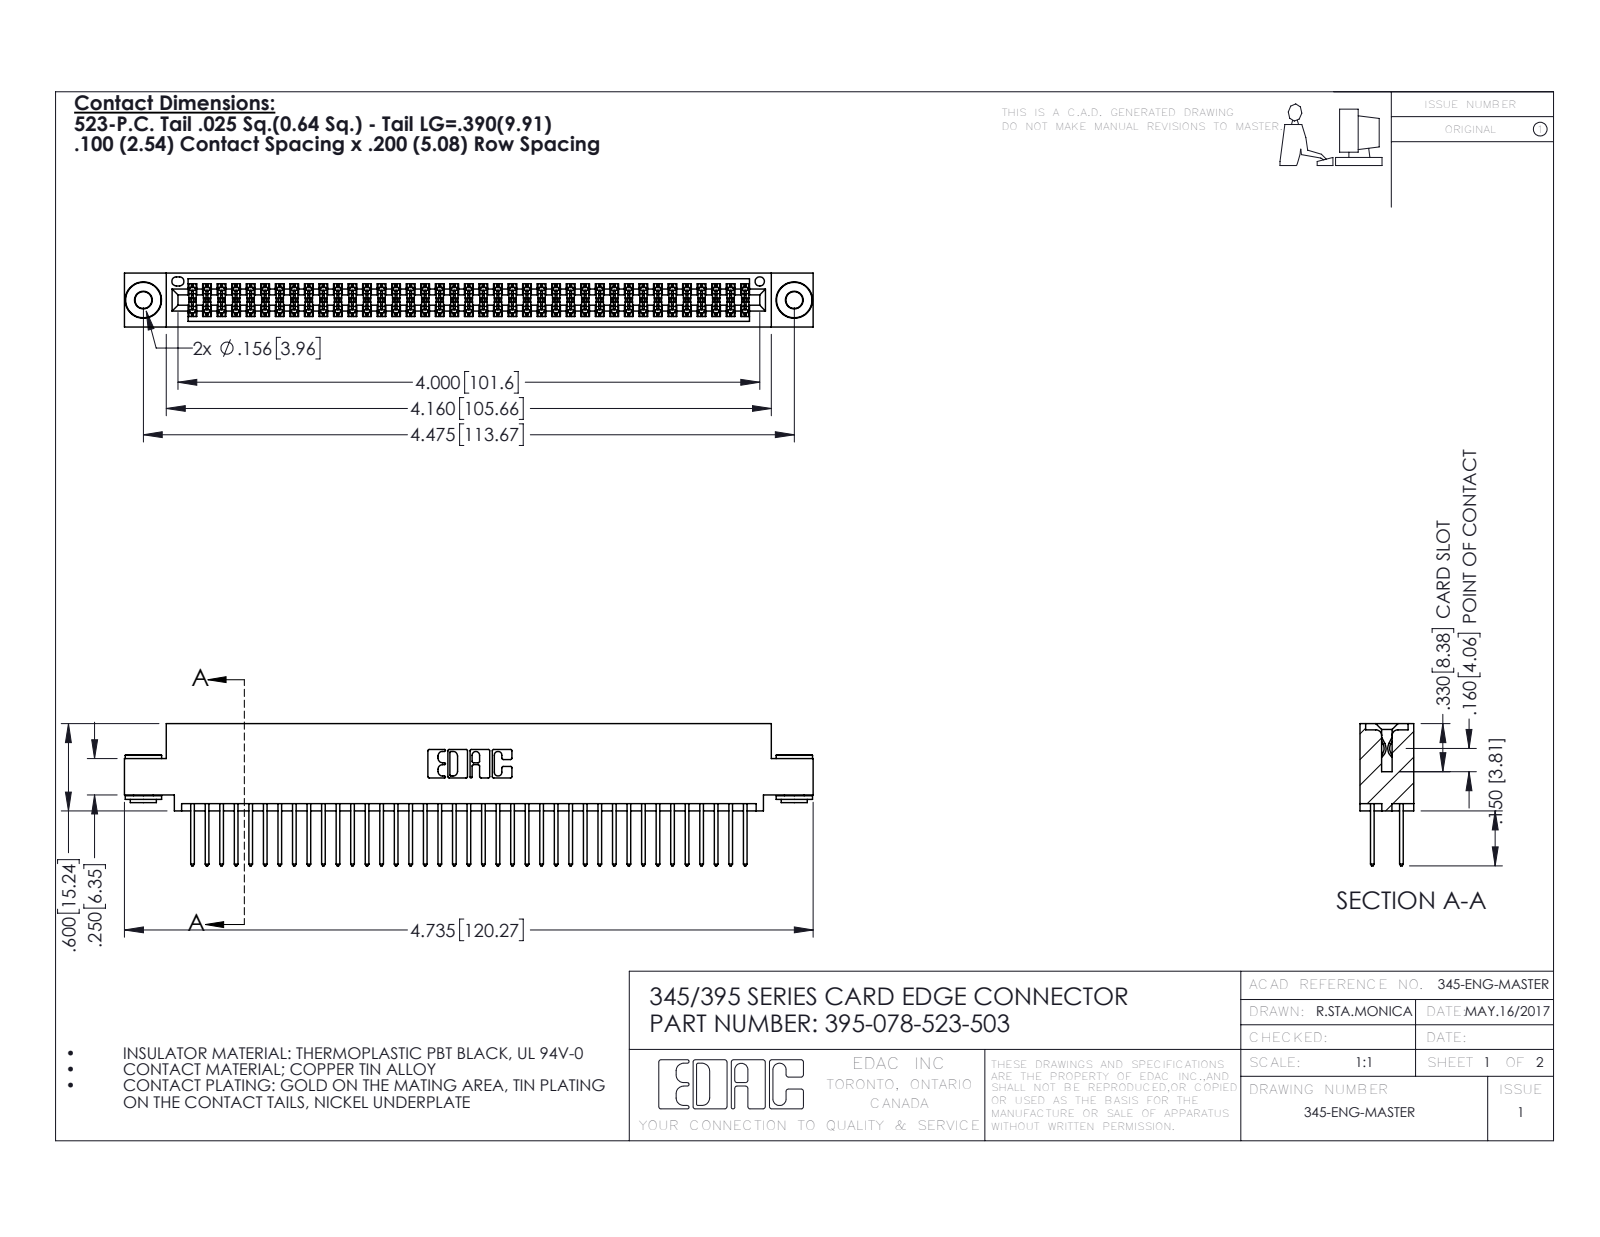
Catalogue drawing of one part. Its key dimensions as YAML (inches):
part_name: "345-292-001_345-293-123; 345-250-002_345-250-002-102; 345 Part_0.110 Offset - 0.156 Dia-TH; 395-078-523-503"
step_written_by: "SolidWorks 2016 (CONFIG_CONTROL_DESIGN)"
units: inches
bodies: {solids: 81, faces: 4068, planar: 2668, cylindrical: 1392, other: 8}
overall_size: [4.735, 0.977, 0.37]
volume: 0.718
surface_area: 28.43
round_holes:
  - {diameter: 0.116, count: 2}
  - {diameter: 0.156, count: 2}
  - {diameter: 0.064, count: 1}
round_bosses_or_shafts:
  - {diameter: 0.25, count: 2}
  - {diameter: 0.18, count: 2}
  - {diameter: 0.136, count: 2}
partial_cylinders:
  - {radius: 0.006, count: 117}
  - {radius: 0.01, count: 78}
  - {radius: 0.01, count: 22}
  - {radius: 0.007, count: 6}
  - {radius: 0.031, count: 6}
  - {radius: 0.026, count: 3}
  - {radius: 0.014, count: 2}
  - {radius: 0.019, count: 2}
face_to_face_distances: [0.072, 0.298, 0.2, 0.025, 0.098, 0.272, 0.37, 0.225, 0.175, 0.149]
hole_center_spacings: [0.27, 4.239, 4.475]
